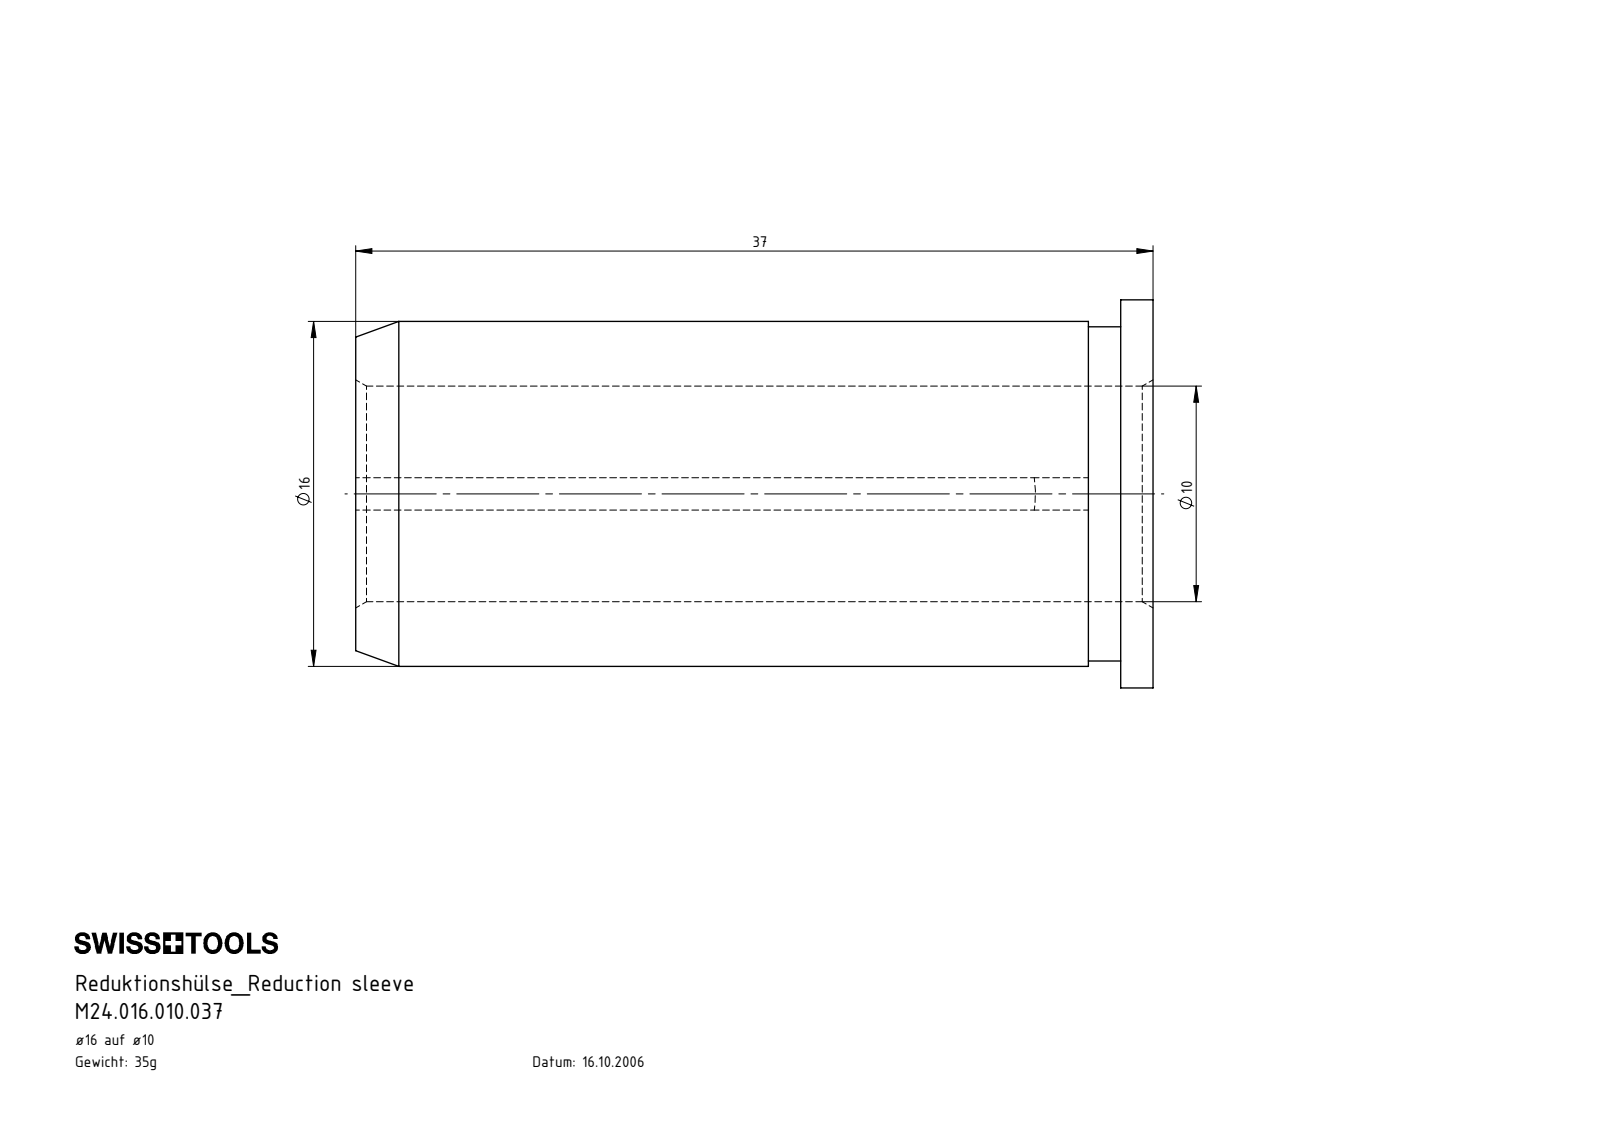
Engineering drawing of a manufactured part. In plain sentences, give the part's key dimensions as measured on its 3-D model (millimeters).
The part is named "U10.U16.001.037". Its 3-D file was written by "SolidWorks 2017 (AUTOMOTIVE_DESIGN)". It is 1 solid with 14 faces: 6 planar, 5 cylindrical and 3 other. Overall it measures 37 by 18 by 18 millimeters. Its volume is 4 408 cubic millimeters and its surface area 3 460 square millimeters. Round holes: 1 of diameter 10. Round bosses or shafts: 1 of diameter 18, 1 of diameter 16, 1 of diameter 15.5. Partial cylindrical surfaces (rounded edges, fillets, slot ends): 1 of radius 31.5. The main face-to-face distances are 1.5, 37, 35.5, 34, 3.
